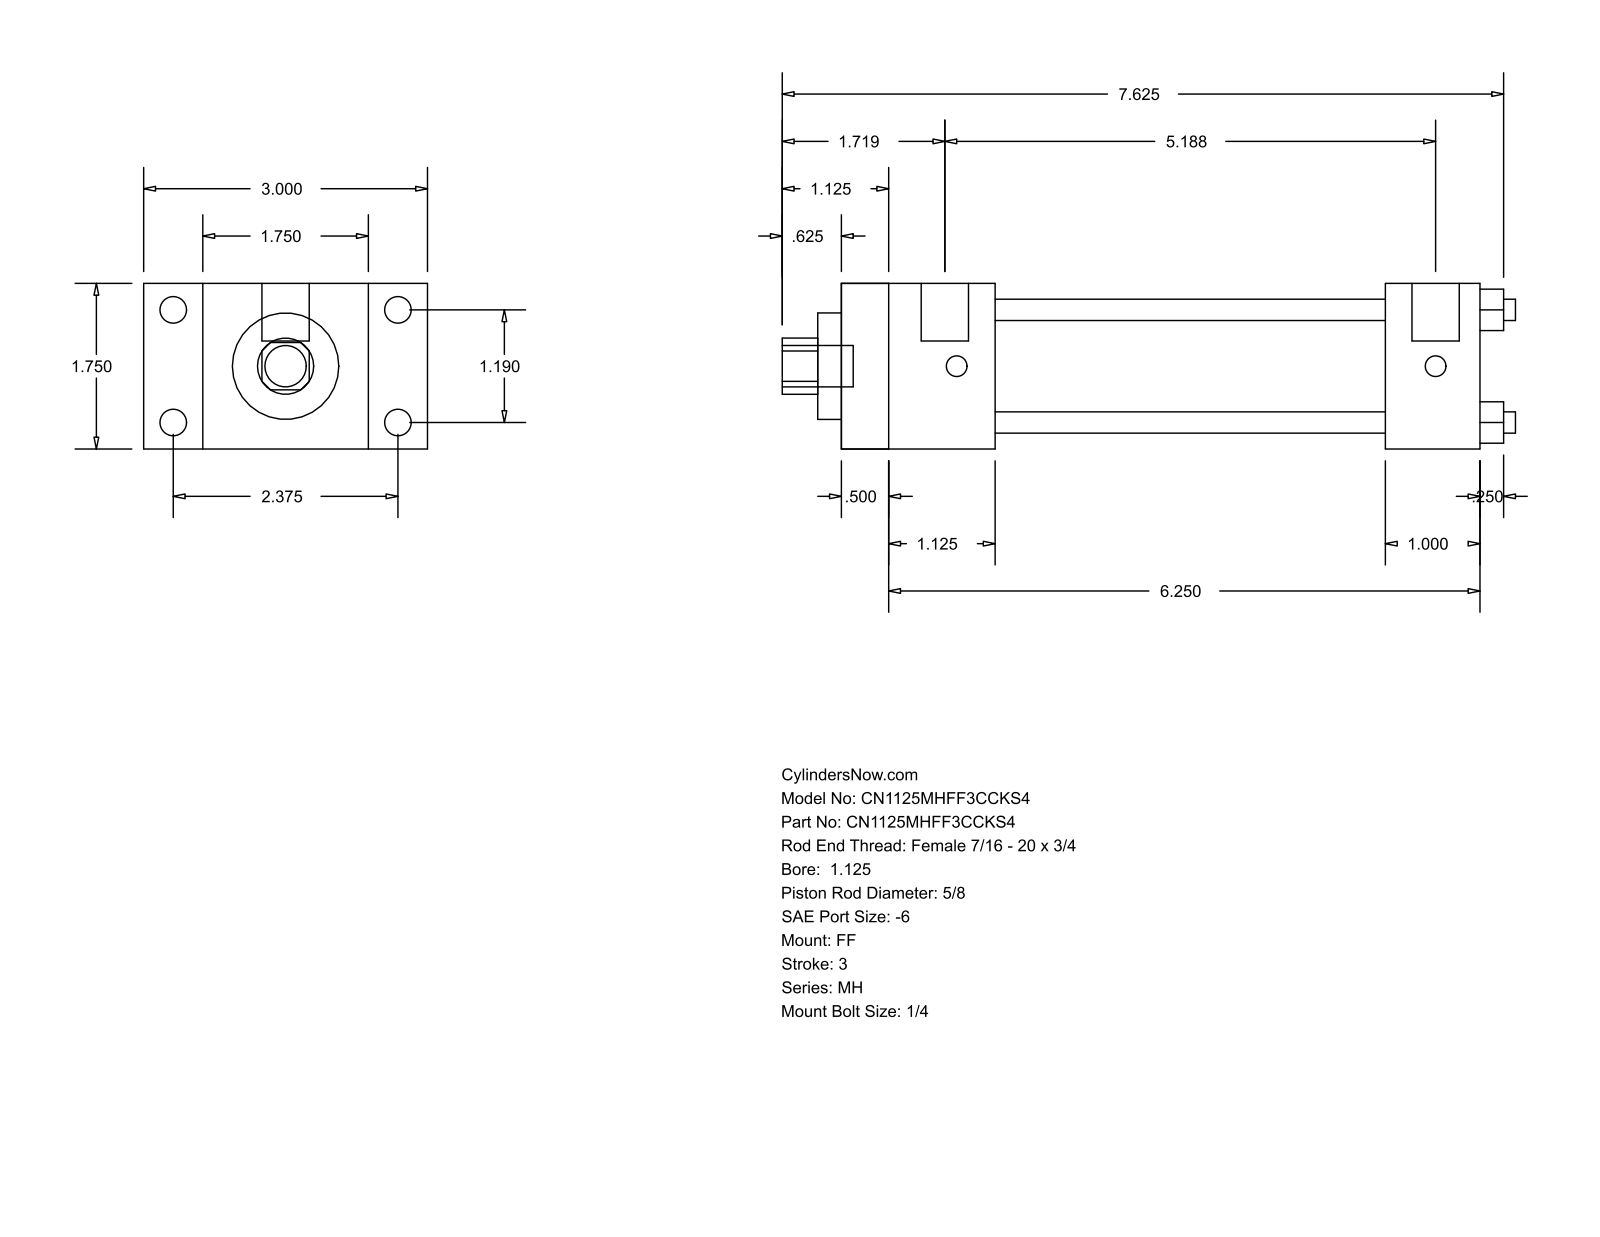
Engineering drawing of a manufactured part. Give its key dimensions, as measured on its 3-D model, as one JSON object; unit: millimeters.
{"part_name": "MH_FF__0112_0.625", "step_written_by": "GSSL Pune (CONFIG_CONTROL_DESIGN)", "units": "millimeters", "bodies": {"solids": 0, "faces": 92, "planar": 64, "cylindrical": 28, "other": 0}, "overall_size": [196.85, 76.2, 44.45], "round_holes": [[5.71, 4], [15.88, 1], [28.57, 1], [34.92, 1]], "round_bosses_or_shafts": [[7.14, 4], [5.56, 4], [12.7, 2], [11.11, 1]], "partial_cylinders_radius": [[7.54, 1]], "face_to_face_distances": [44.46, 171.44, 12.69, 158.75, 15.87, 60.33, 28.58, 41.27, 146.05, 133.36], "hole_center_spacings": [21.37, 30.22, 42.74]}
